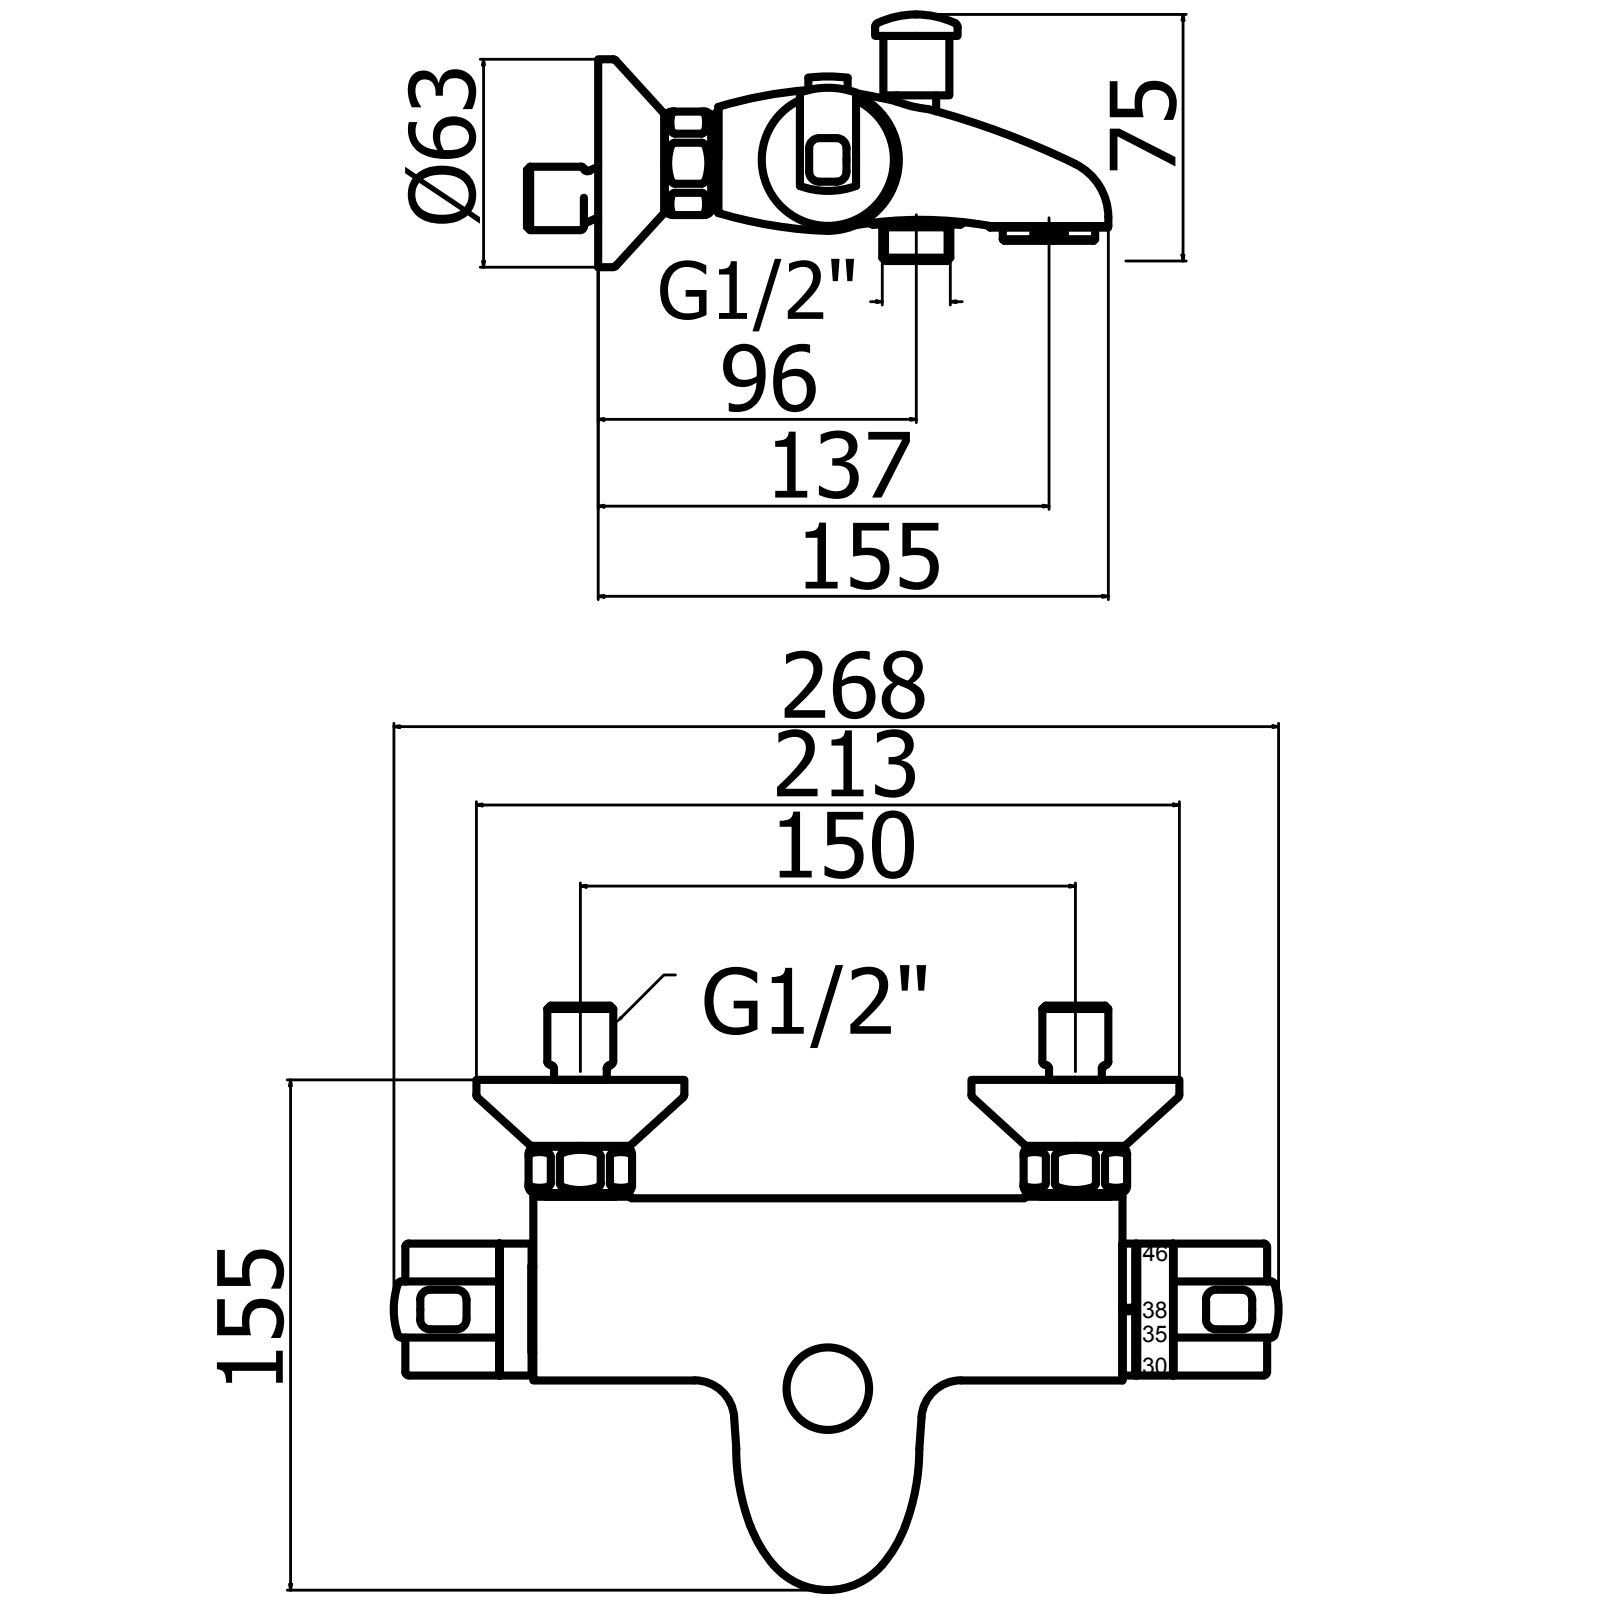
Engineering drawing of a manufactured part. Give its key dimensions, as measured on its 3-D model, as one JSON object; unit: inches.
{"part_name": "CORPO VASCA; MANIGLIA DESTRA; MANIGLIA SINISTRA; ROSONE (+1 more)", "step_written_by": "Autodesk Inventor 2016 (AUTOMOTIVE_DESIGN)", "units": "inches", "bodies": {"solids": 7, "faces": 265, "planar": 90, "cylindrical": 104, "other": 71}, "overall_size": [10.394, 6.528, 2.982], "volume_in3": 33.75, "surface_area_in2": 135.3, "round_holes": [[2.378, 2], [0.787, 1], [1.378, 1]], "round_bosses_or_shafts": [[2.5, 2], [0.827, 2], [0.079, 2], [1.575, 1], [1.142, 1], [1.102, 1], [0.945, 1], [0.787, 1]], "partial_cylinders_radius": [[0.01, 24], [0.236, 12], [0.118, 8], [0.039, 4], [0.591, 4], [0.276, 2], [0.787, 2], [0.079, 1]], "face_to_face_distances": [0.039, 7.126, 0.079, 7.087, 0.591, 1.496, 7.165, 1.614, 8.661, 8.74], "hole_center_spacings": [5.906]}
